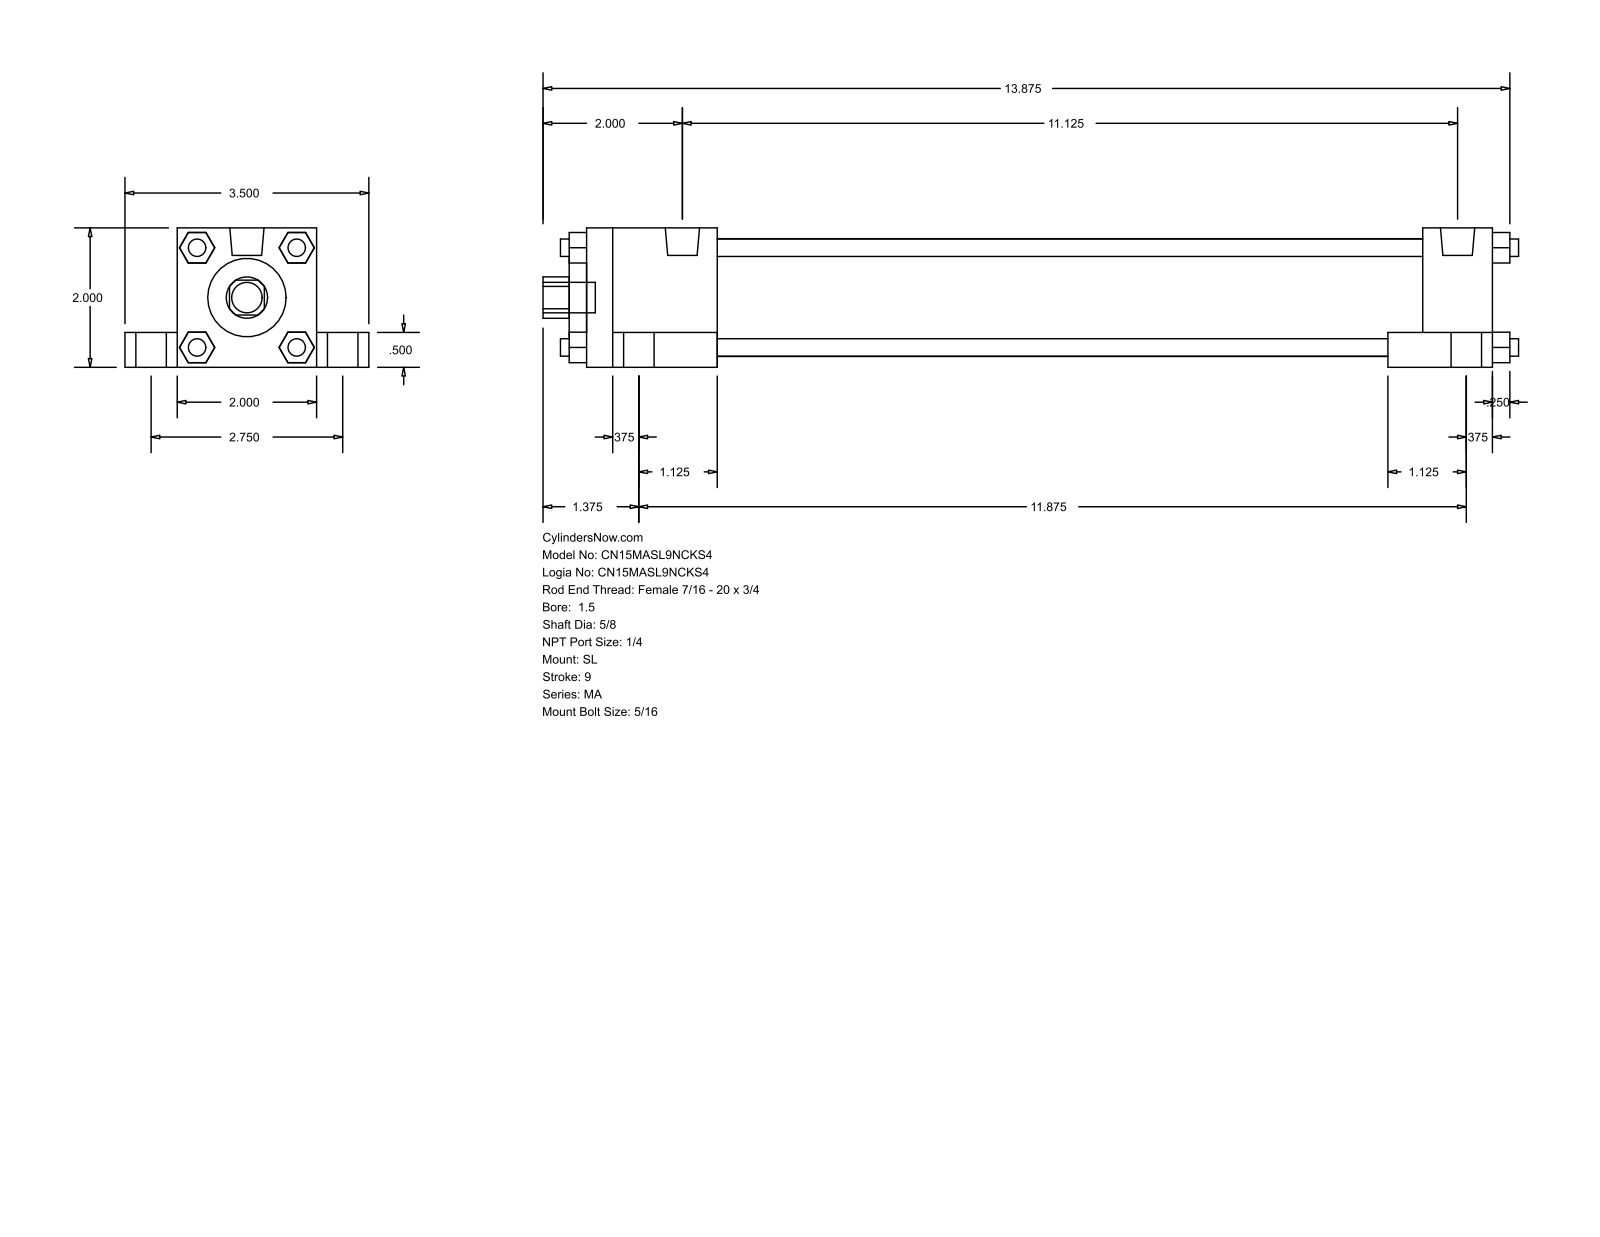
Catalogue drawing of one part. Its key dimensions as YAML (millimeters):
part_name: "MA_SL__0150_0.625"
step_written_by: "GSSL Pune (CONFIG_CONTROL_DESIGN)"
units: millimeters
bodies: {solids: 0, faces: 148, planar: 112, cylindrical: 36, other: 0}
overall_size: [355.6, 88.9, 50.8]
round_holes:
  - {diameter: 15.88, count: 1}
  - {diameter: 28.57, count: 1}
  - {diameter: 42.93, count: 1}
round_bosses_or_shafts:
  - {diameter: 11.11, count: 5}
  - {diameter: 17.46, count: 4}
  - {diameter: 7.94, count: 4}
  - {diameter: 6.35, count: 4}
  - {diameter: 12.49, count: 2}
partial_cylinders:
  - {radius: 7.54, count: 1}
face_to_face_distances: [50.8, 19.05, 38.1, 12.7, 69.85, 330.19, 9.52, 304.8, 25.39, 47.62]
